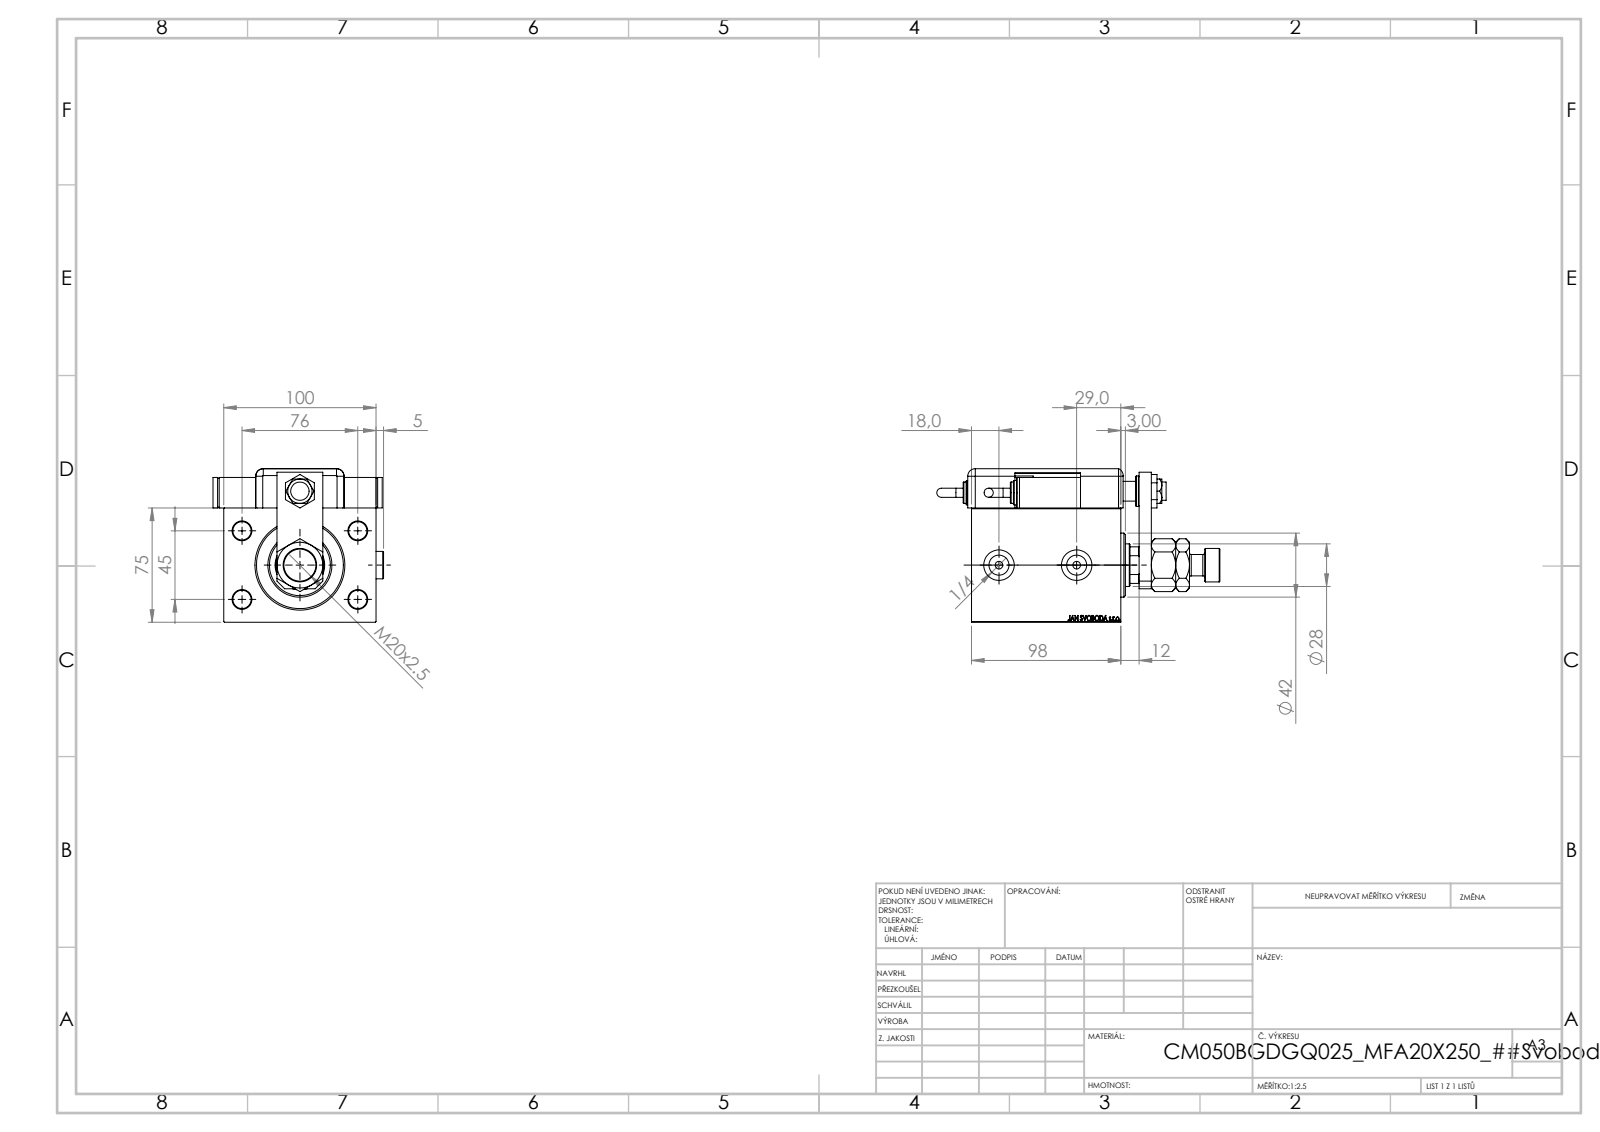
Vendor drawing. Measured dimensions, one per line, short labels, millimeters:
name: SWITCH_Q_FRONT_BACK; TYC; V450CM_B_Body; ZARAZKA_Q (+7 more)
written by: SolidWorks 2019 (CONFIG_CONTROL_DESIGN)
unit: mm
bodies: 16 solids, 1374 faces (658 planar, 131 cylindrical, 585 other)
size: 185.76 × 111.9 × 100.8
volume: 843 932 mm³; area: 157 559 mm²
holes: 5× ⌀12, 3× ⌀20, 2× ⌀4, 2× ⌀5, 2× ⌀8, 2× ⌀13.16, 1× ⌀13, 1× ⌀14, 1× ⌀18.5, 1× ⌀28, 1× ⌀31.5, 1× ⌀32.5
bosses: 3× ⌀20, 3× ⌀14, 2× ⌀18, 2× ⌀16, 2× ⌀6, 1× ⌀42, 1× ⌀22
rounds: 9× R5, 1× R10, 1× R13.5
face distances: 75, 3, 98, 100, 20, 14, 84, 25.8, 100.8, 13.5
hole spacings: 44.16, 45, 46.04, 76, 80.53, 88.32, 20, 48.5
